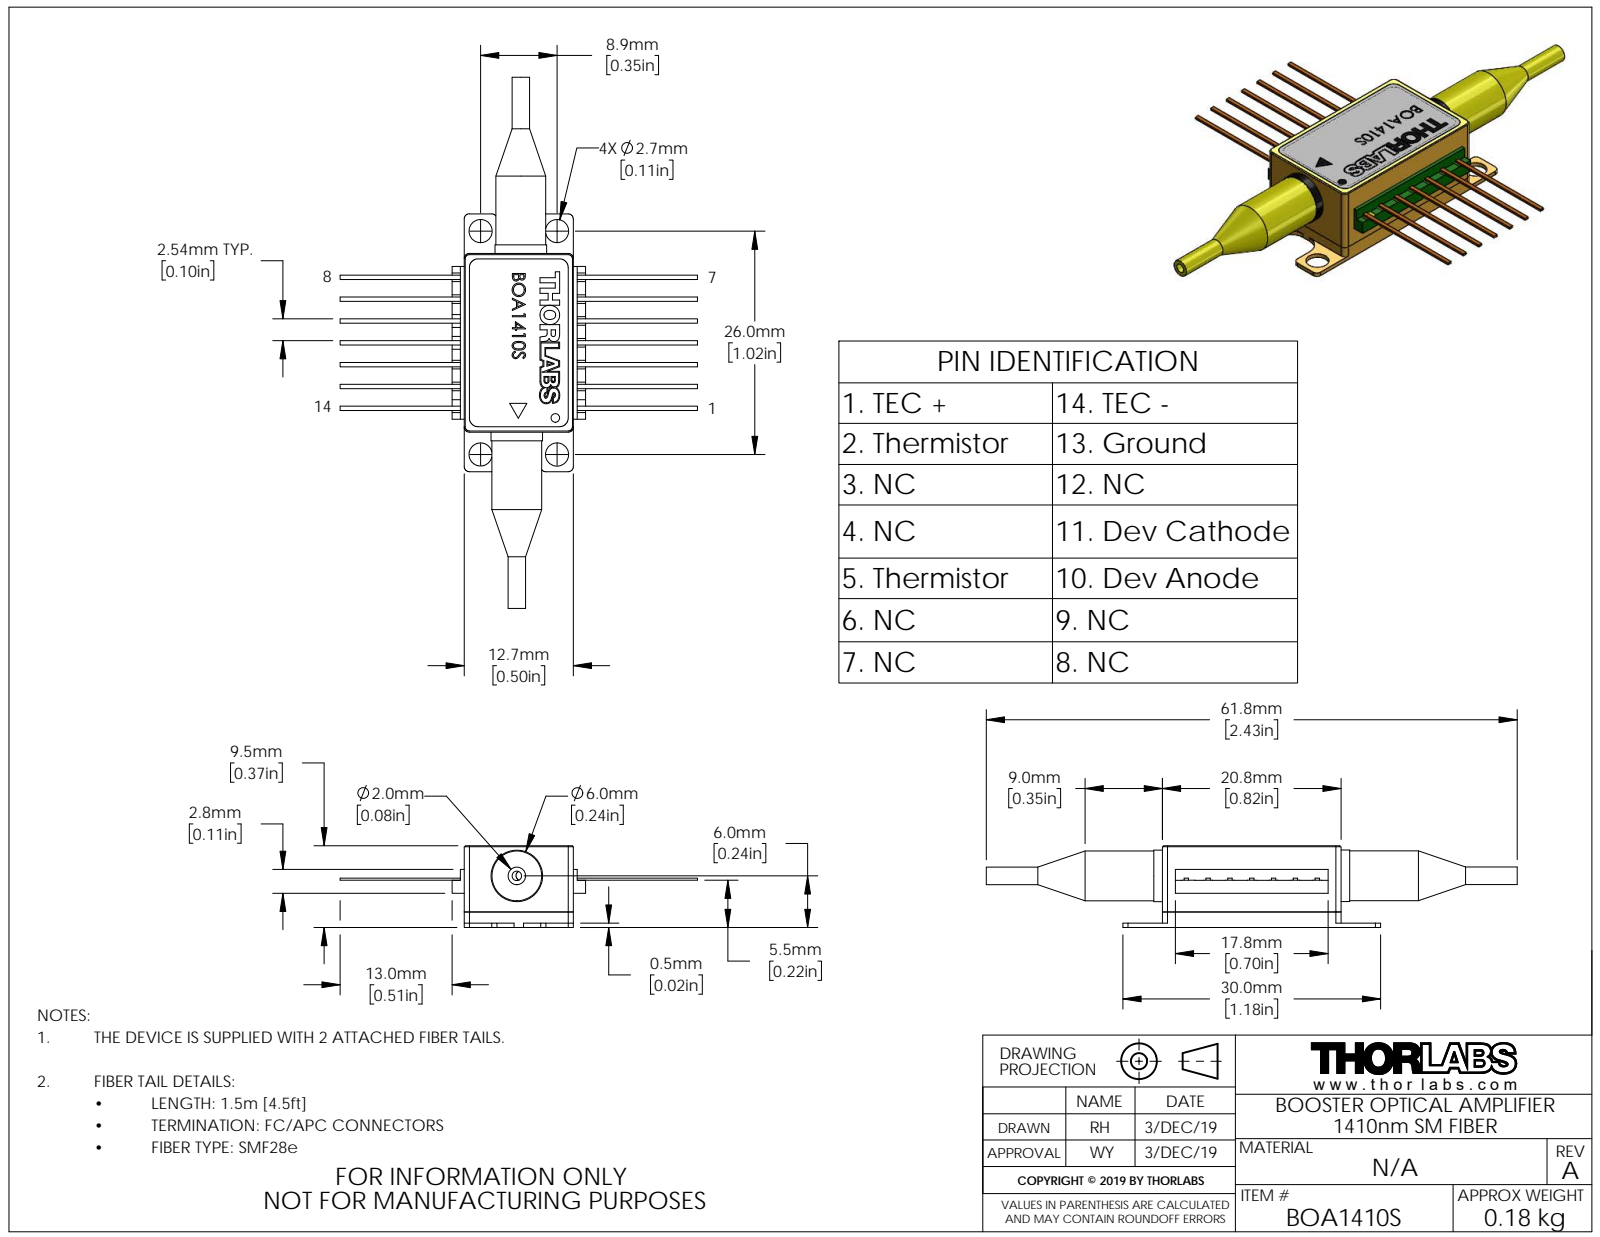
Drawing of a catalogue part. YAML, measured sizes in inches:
part_name: "QTN039251-E0W"
step_written_by: "SolidWorks 2018 (AUTOMOTIVE_DESIGN)"
units: inches
bodies: {solids: 0, faces: 355, planar: 252, cylindrical: 54, other: 49}
overall_size: [2.433, 1.638, 0.374]
round_holes:
  - {diameter: 0.106, count: 4}
  - {diameter: 0.043, count: 2}
  - {diameter: 0.039, count: 1}
round_bosses_or_shafts:
  - {diameter: 0.236, count: 2}
  - {diameter: 0.228, count: 2}
  - {diameter: 0.08, count: 2}
partial_cylinders:
  - {radius: 0.024, count: 12}
  - {radius: 0.02, count: 4}
  - {radius: 0.039, count: 4}
  - {radius: 0.079, count: 4}
face_to_face_distances: [0.373, 0.5, 0.156, 0.217, 0.217, 0.06, 0.157, 0.02, 0.226, 0.07]
hole_center_spacings: [0.35, 1.024, 1.082, 0.019, 0.168, 0.381, 0.856, 0.922]
